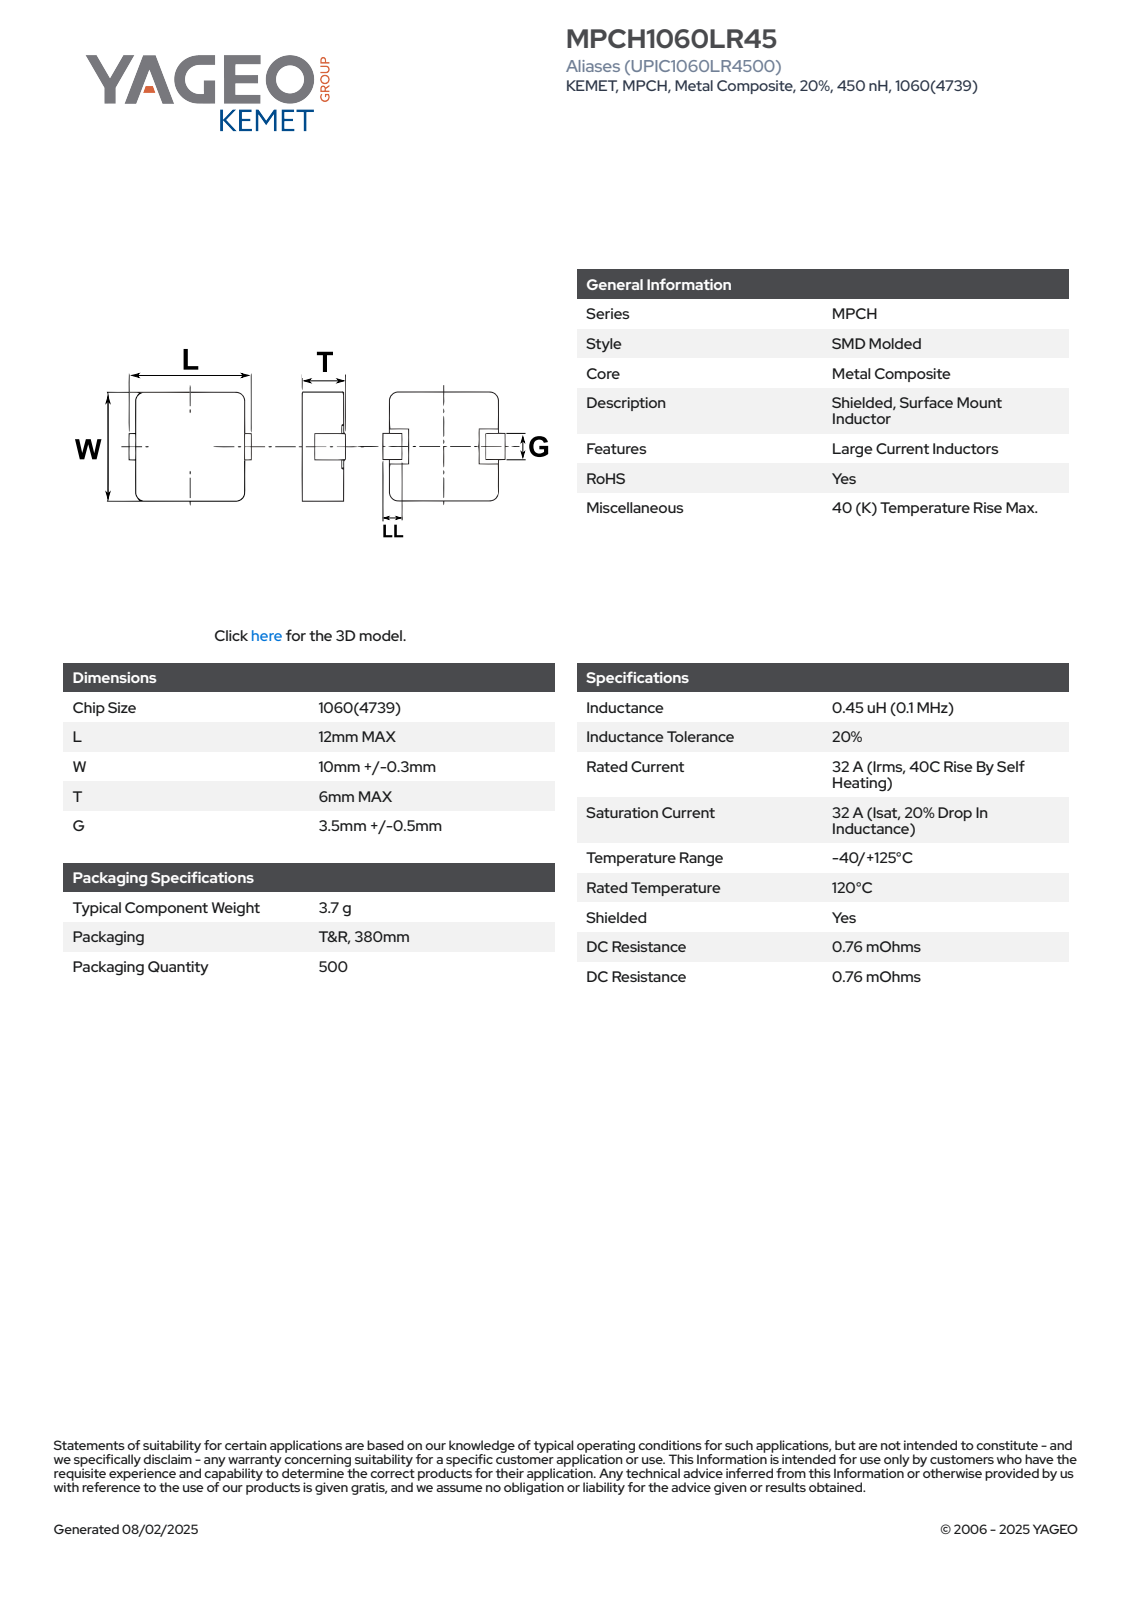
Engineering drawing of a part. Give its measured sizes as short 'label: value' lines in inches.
name: IS_MPC_4739_L12W10.3T6LL2.1G4
written by: SolidWorks 2014 (AUTOMOTIVE_DESIGN)
unit: in
bodies: 4 solids, 105 faces (93 planar, 12 cylindrical, 0 other)
size: 0.472 × 0.406 × 0.236
volume: 0.043 in³; area: 0.882 in²
rounds: 4× R0.035
face distances: 0.234, 0.406, 0.456, 0.465, 0.464, 0.469, 0.46, 0.461, 0.456, 0.457
